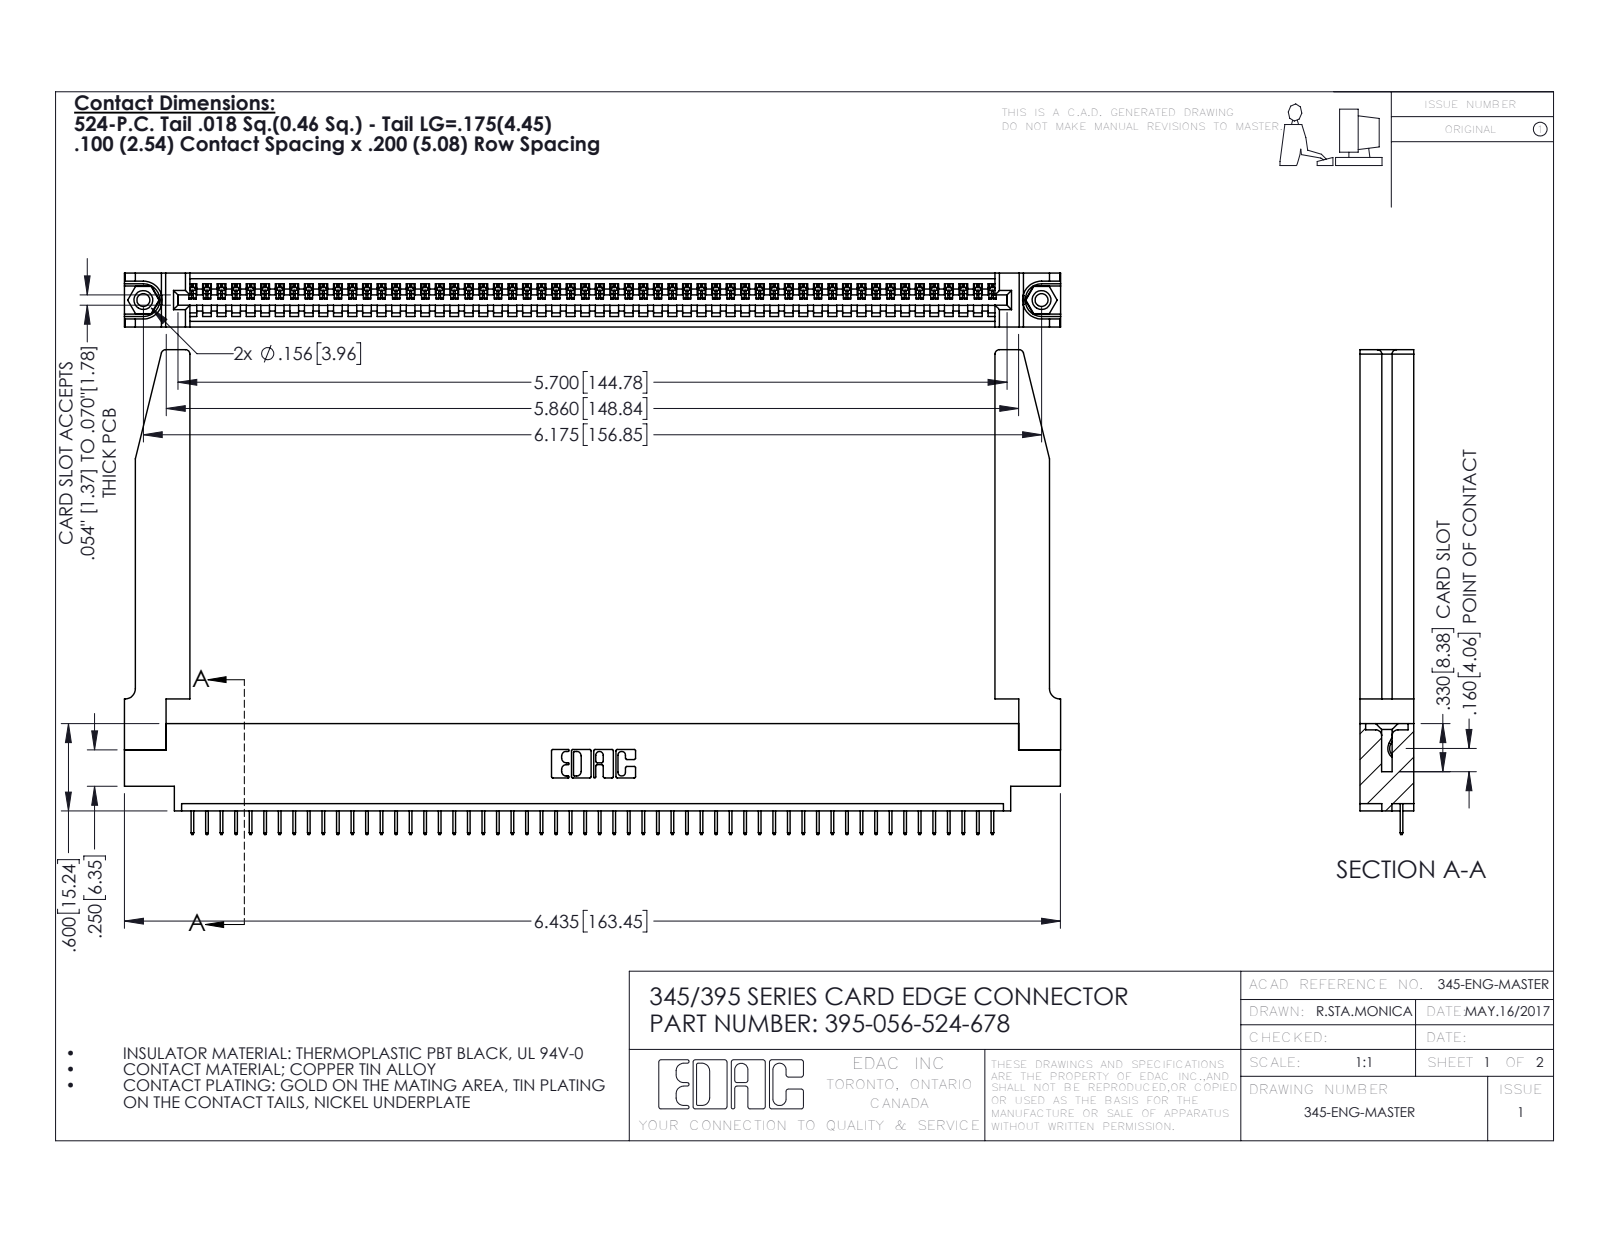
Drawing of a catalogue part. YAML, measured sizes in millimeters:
part_name: "345-292-001_345-293-124; 345-250-001_345-250-001-102; 345-220-078_345-220-078; 395-056-524-678 (+1 more)"
step_written_by: "SolidWorks 2016 (CONFIG_CONTROL_DESIGN)"
units: millimeters
bodies: {solids: 61, faces: 3836, planar: 2802, cylindrical: 982, other: 52}
overall_size: [163.5, 84.6, 9.4]
volume: 23070
surface_area: 26800
round_holes:
  - {diameter: 2.3, count: 2}
  - {diameter: 3.2, count: 2}
  - {diameter: 4, count: 2}
  - {diameter: 1.6, count: 1}
round_bosses_or_shafts:
  - {diameter: 3.9, count: 2}
partial_cylinders:
  - {radius: 0.2, count: 112}
  - {radius: 0.3, count: 22}
  - {radius: 0.8, count: 8}
  - {radius: 0.2, count: 6}
  - {radius: 0.8, count: 6}
  - {radius: 0.7, count: 3}
  - {radius: 0.8, count: 2}
  - {radius: 1, count: 2}
face_to_face_distances: [9.4, 1.8, 7.6, 2.5, 6.9, 0.6, 5.1, 5.7, 1.8, 3.8]
hole_center_spacings: [6.9, 150.9, 156.8]
